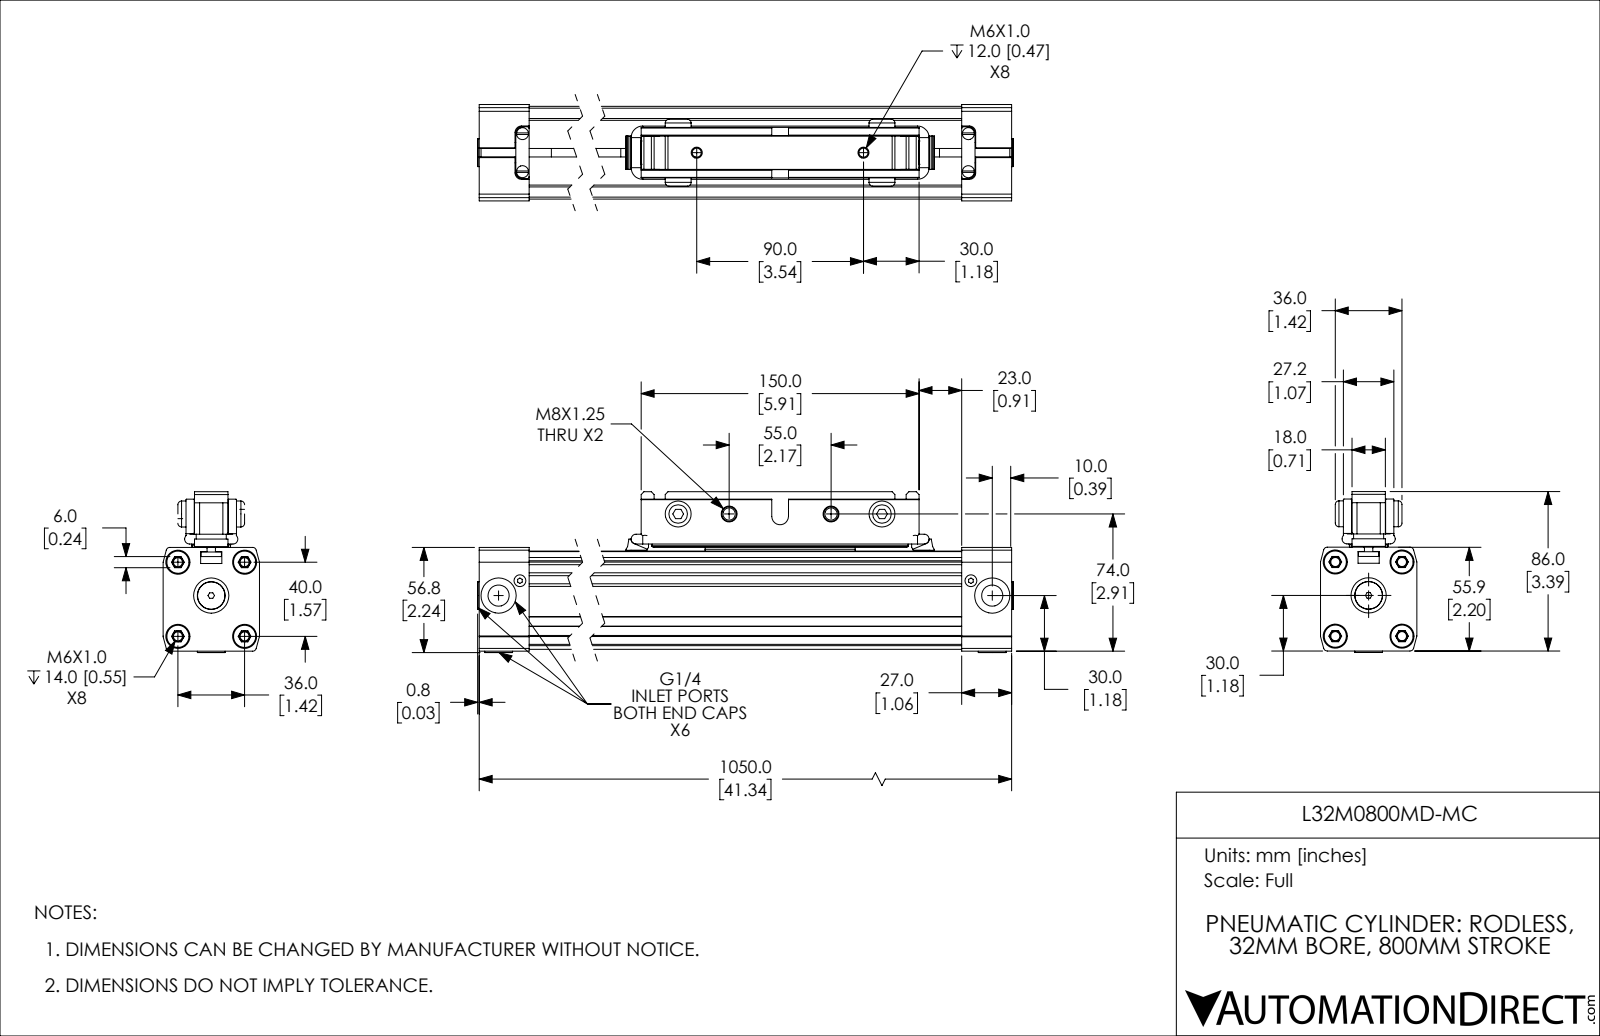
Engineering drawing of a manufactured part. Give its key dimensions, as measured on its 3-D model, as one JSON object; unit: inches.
{"part_name": "L32M0800MD-MC_PISTON; L32M0800MD-MC; L32M0800MD-MC_BODY", "step_written_by": "SolidWorks 2019 (CONFIG_CONTROL_DESIGN)", "units": "inches", "bodies": {"solids": 13, "faces": 822, "planar": 433, "cylindrical": 273, "other": 116}, "overall_size": [41.4, 3.417, 2.047], "volume_in3": 117.3, "surface_area_in2": 715.3, "round_holes": [[0.194, 6], [0.451, 5], [0.748, 5], [0.256, 4], [0.262, 4], [0.339, 4], [0.512, 4], [0.252, 2], [1.264, 1]], "round_bosses_or_shafts": [[0.472, 4], [0.21, 4], [0.591, 3], [0.383, 3], [0.323, 3], [0.551, 2], [1.26, 1], [1.252, 1]], "partial_cylinders_radius": [[0.039, 22], [0.079, 18], [0.138, 8], [0.012, 4], [0.02, 4], [0.024, 4], [0.157, 4], [0.006, 2]], "face_to_face_distances": [2.087, 1.969, 0.201, 1.072, 0.445, 0.894, 1.075, 0.181, 1.768, 0.454], "hole_center_spacings": [0.649, 40.006, 0.552, 0.807, 0.935, 1.002, 1.083, 1.119]}
